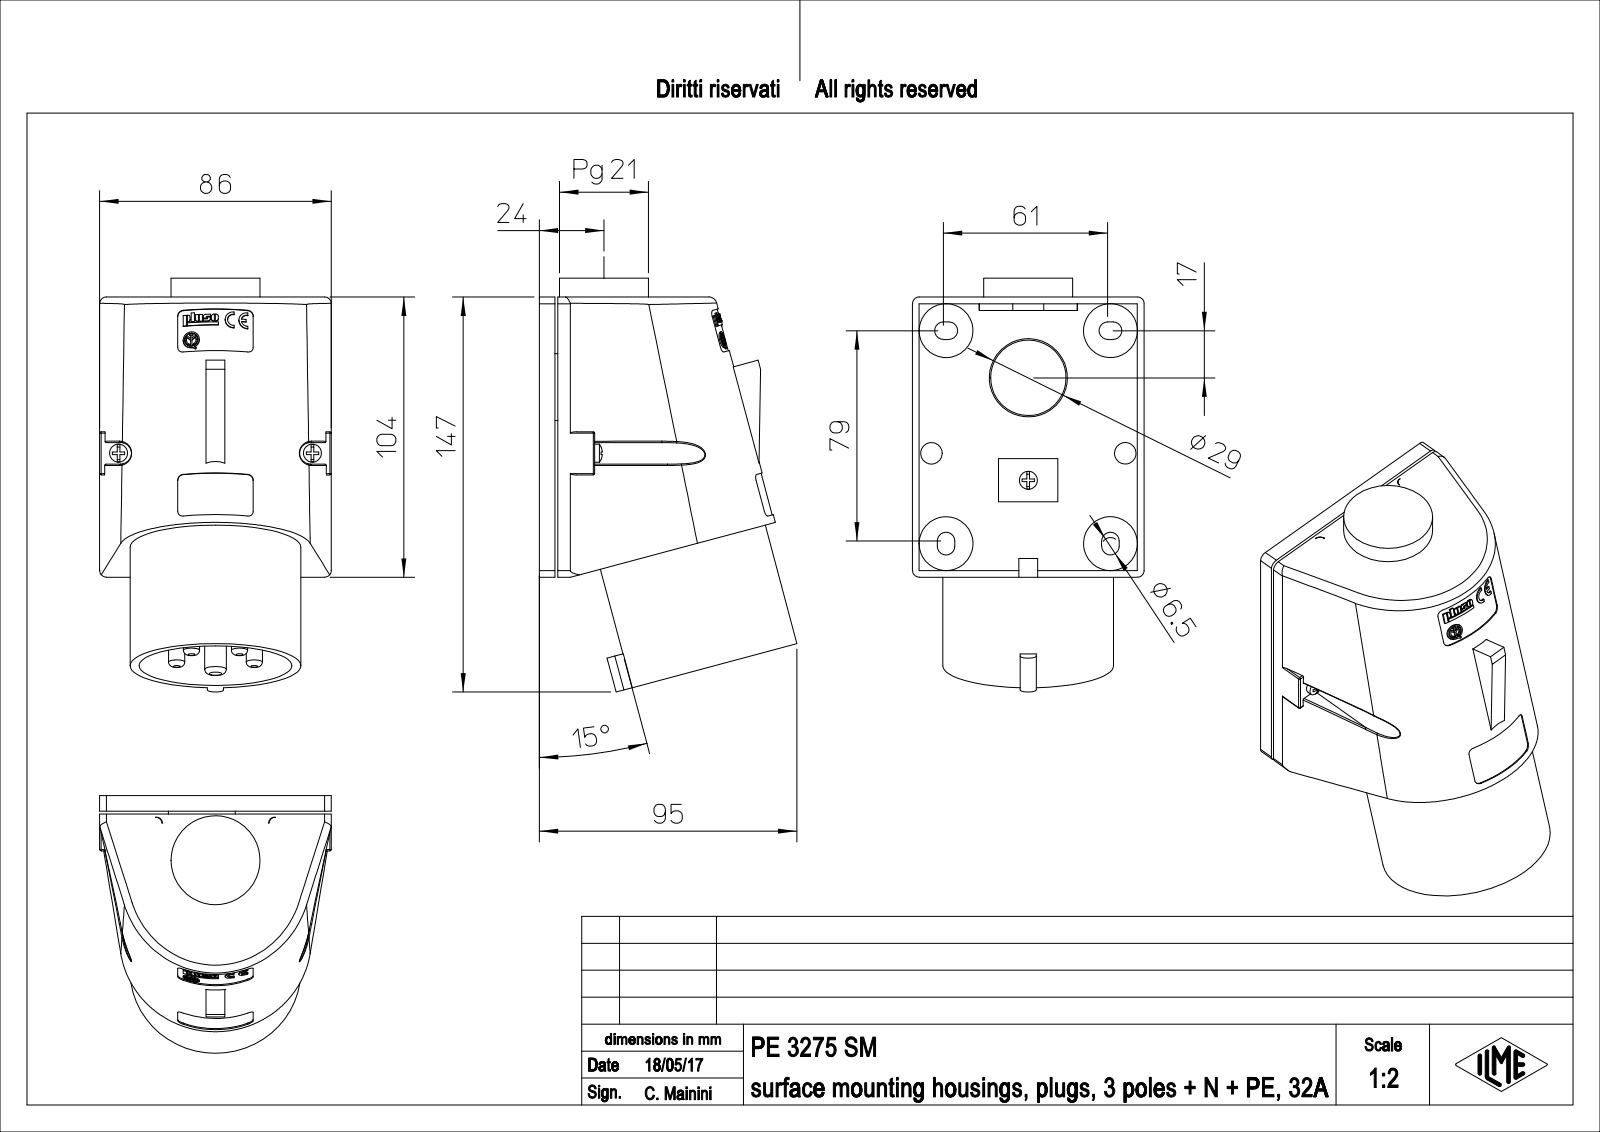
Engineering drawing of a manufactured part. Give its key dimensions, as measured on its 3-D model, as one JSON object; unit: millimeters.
{"part_name": "PE_3275_SM", "step_written_by": "PTC Creo Elements/Direct Modeling 19.0E 27-Jun-2016 (C) Parametric Technology GmbH (AUTOMOTIVE_DESIGN)", "units": "millimeters", "bodies": {"solids": 1, "faces": 1055, "planar": 668, "cylindrical": 220, "other": 167}, "overall_size": [153.55, 95.62, 86], "volume_mm3": 518948, "surface_area_mm2": 96274, "round_holes": [[6.1, 4], [2.8, 2], [3.2, 2], [4, 2], [4.5, 2], [4.2, 1], [5.04, 1], [27.54, 1], [29, 1], [32, 1], [56.7, 1]], "round_bosses_or_shafts": [[6.7, 5], [6, 5], [20, 4], [8, 3], [3, 2], [63.4, 1], [33, 1], [24.84, 1]], "partial_cylinders_radius": [[0.5, 20], [0.17, 11], [2, 10], [0.86, 9], [3.25, 8], [2.5, 6], [0.75, 4], [4.5, 4]], "face_to_face_distances": [1.07, 4.75, 5.82, 7, 1, 5.75, 6.82, 2.25, 2.5, 8], "hole_center_spacings": [15.15, 72, 17.81, 21.93, 24.8, 28.81, 37.36, 37.37]}
